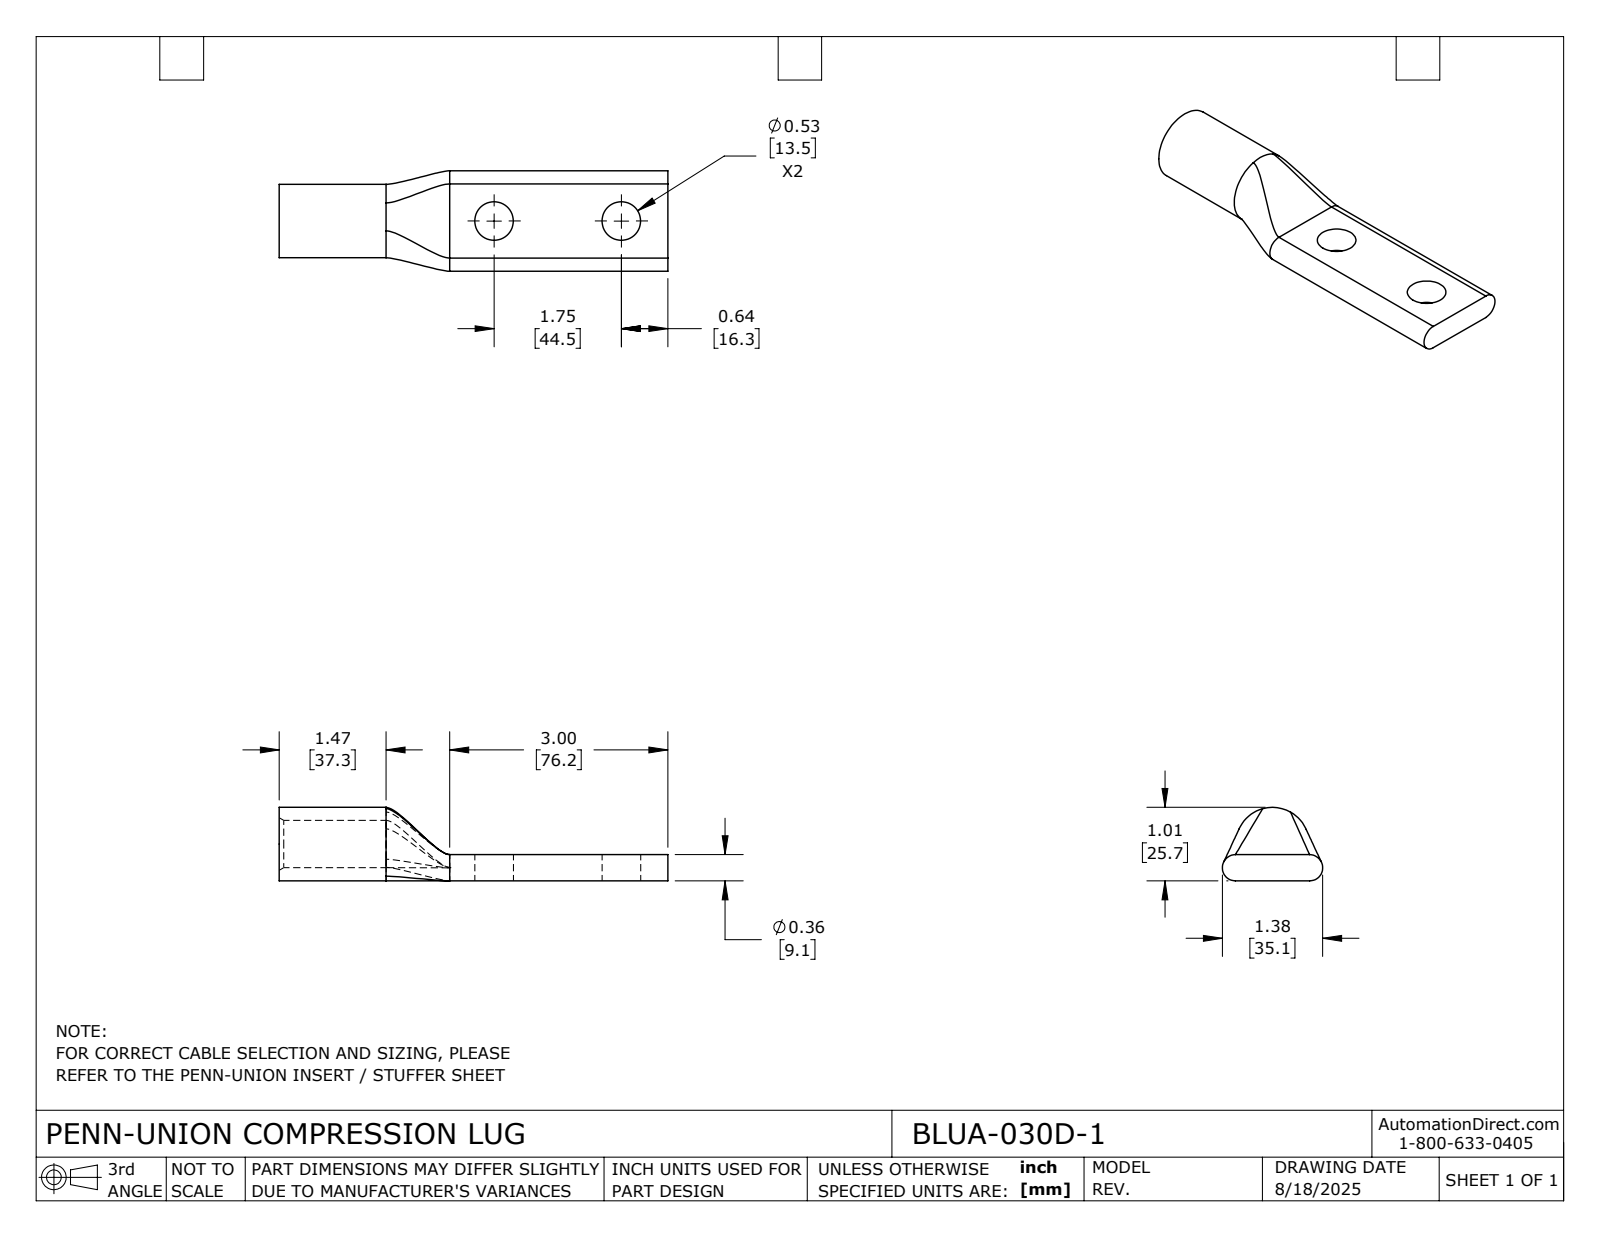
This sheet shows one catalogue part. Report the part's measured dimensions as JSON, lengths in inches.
{"part_name": "BLUA-030D-1", "step_written_by": "SolidWorks 2024 (CONFIG_CONTROL_DESIGN)", "units": "inches", "bodies": {"solids": 1, "faces": 26, "planar": 5, "cylindrical": 11, "other": 10}, "overall_size": [5.343, 1.38, 1.01], "volume_in3": 2.342, "surface_area_in2": 23.27, "round_holes": [[0.531, 2], [0.65, 1]], "round_bosses_or_shafts": [[1.01, 1]], "partial_cylinders_radius": [[0.18, 2]], "face_to_face_distances": [0.36, 5.343, 2.343, 3], "hole_center_spacings": [1.75]}
